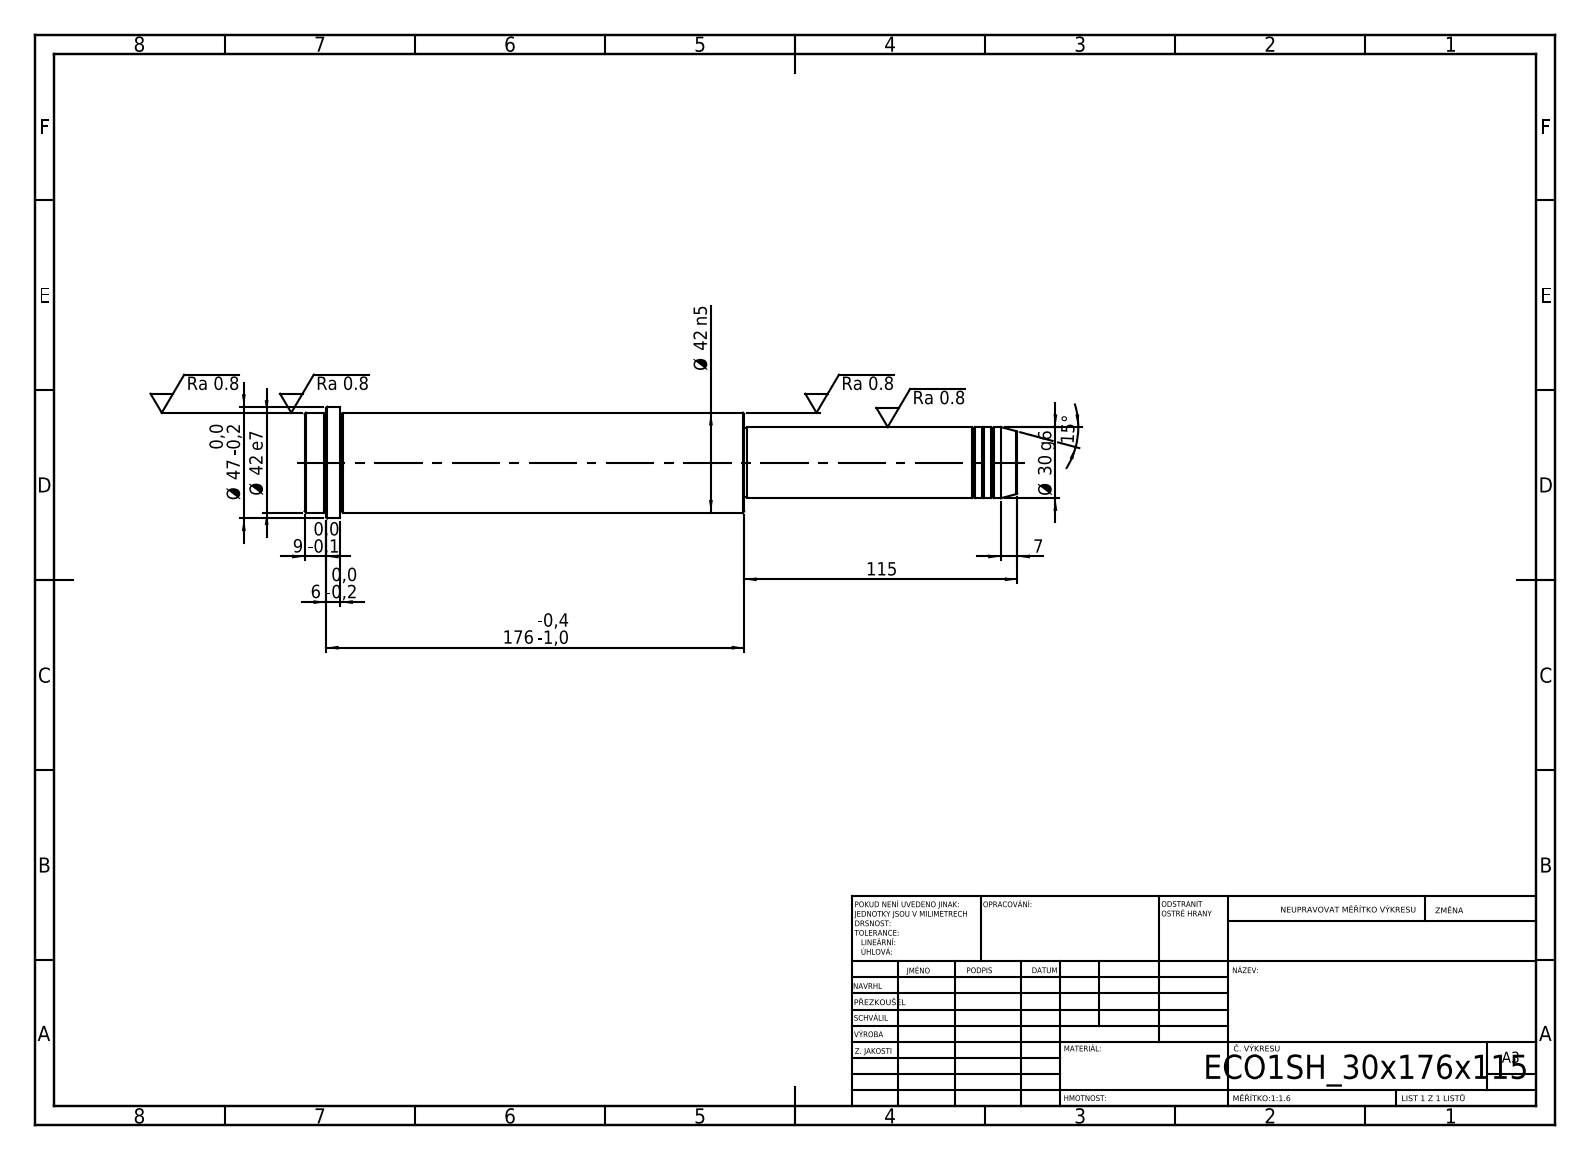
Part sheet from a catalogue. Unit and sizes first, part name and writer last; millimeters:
Units: millimetres
Overall size (bounding box): 300 × 47 × 47
Round bosses / shafts (diameter × count): ⌀47 ×1, ⌀42 ×1, ⌀30 ×1, ⌀29 ×1
Main face-to-face distances: 185, 115, 300, 285, 170, 15, 291, 176, 6, 9
Volume: 338 788 mm³ · Surface area: 38 883 mm²
Bodies: 1 solid, 52 faces (6 planar, 16 cylindrical, 30 other)
STEP written by: SolidWorks 2019 (CONFIG_CONTROL_DESIGN)
